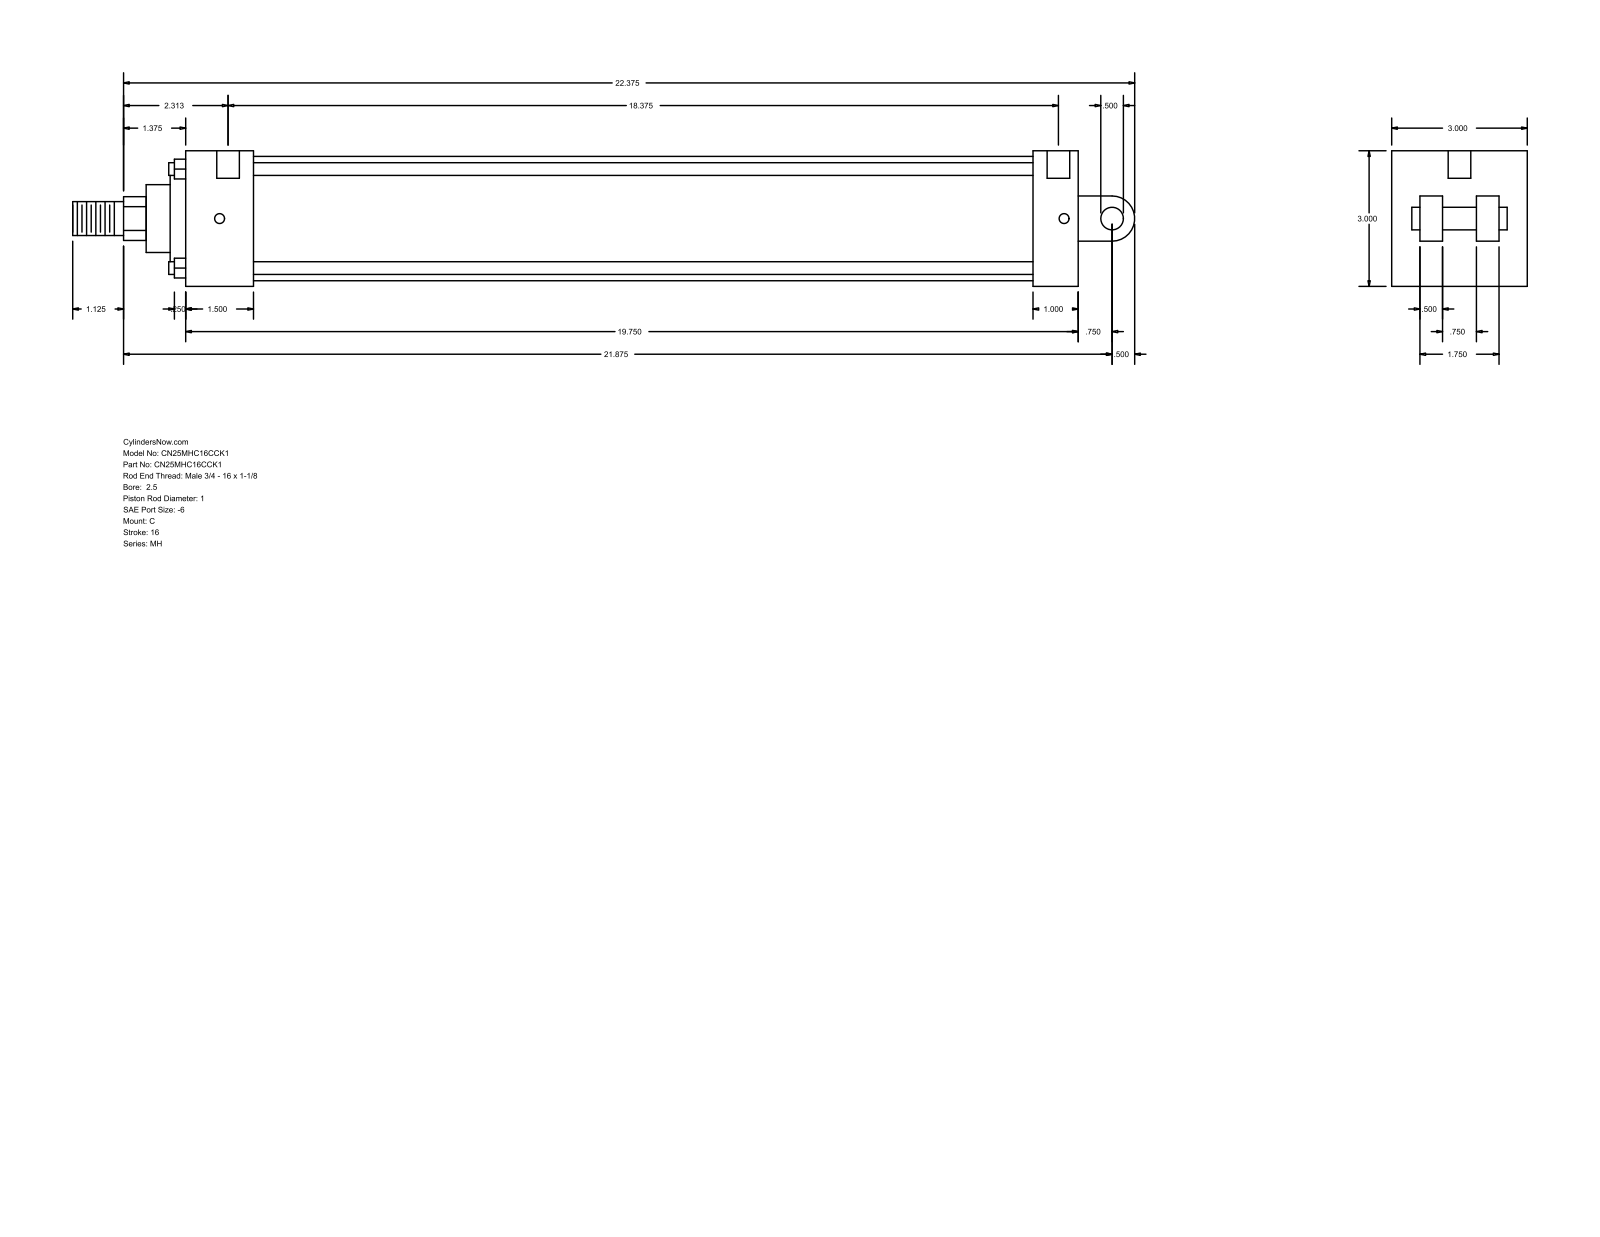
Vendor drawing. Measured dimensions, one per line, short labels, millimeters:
name: MH_C__0250_1
written by: GSSL Pune (CONFIG_CONTROL_DESIGN)
unit: mm
bodies: 0 solids, 101 faces (71 planar, 30 cylindrical, 0 other)
size: 596.9 × 76.2 × 76.2
holes: 4× ⌀5.56, 2× ⌀12.7
bosses: 4× ⌀7.14, 1× ⌀69.85, 1× ⌀60.33, 1× ⌀38.1, 1× ⌀25.4, 1× ⌀19.05, 1× ⌀12.7
rounds: 1× R12.29, 1× R12.7
face distances: 76.2, 25.4, 501.66, 60.33, 15.87, 476.26, 38.11, 438.15, 463.55, 12.7
hole spacings: 474.66, 3.18, 4.76, 466.72, 469.9, 471.48
